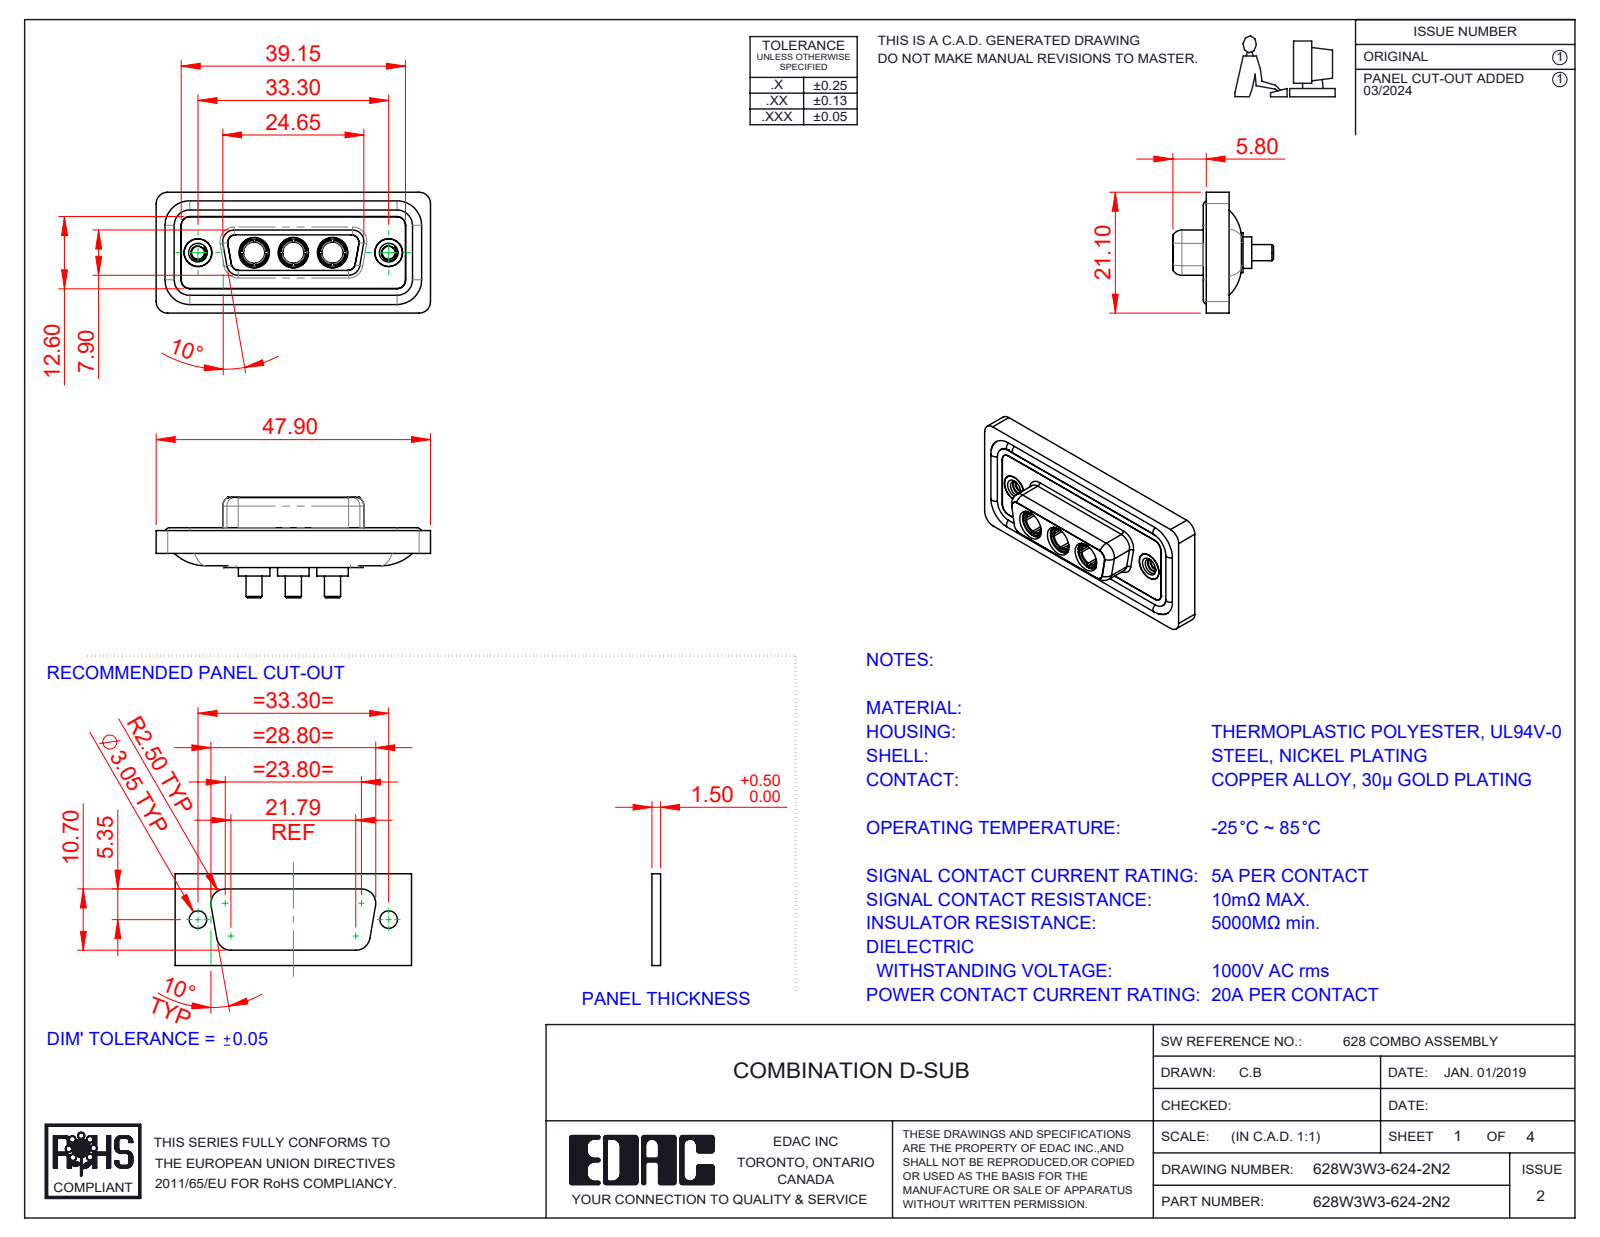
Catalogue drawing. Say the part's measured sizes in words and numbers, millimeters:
The part is named "628Combo Housing_3W3; 628Combo Threaded Rivet_2; 628Combo Waterproof Housing_15 Contacts; 628Combo Shell Rear_15 Contacts (+3 more)". Its 3-D file was written by "SolidWorks 2023 (CONFIG_CONTROL_DESIGN)". It is 13 solids with 608 faces: 192 planar, 257 cylindrical and 159 other. Overall it measures 47.9 by 21.1 by 17.55 millimeters. Its volume is 6 026 cubic millimeters and its surface area 9 739 square millimeters. Round holes: 5 of diameter 4.85, 3 of diameter 3.7, 3 of diameter 5.3, 2 of diameter 2.26, 2 of diameter 4, 2 of diameter 4.05, 2 of diameter 5. Round bosses or shafts: 4 of diameter 1.6, 3 of diameter 5.5, 3 of diameter 5.2, 3 of diameter 4.96, 3 of diameter 4.75, 3 of diameter 3.75, 3 of diameter 2.8, 2 of diameter 4.95. Partial cylindrical surfaces (rounded edges, fillets, slot ends): 22 of radius 1.5, 20 of radius 2, 12 of radius 1.35, 8 of radius 1.6, 4 of radius 0.25, 4 of radius 0.5, 4 of radius 0.6, 4 of radius 0.65. The main face-to-face distances are 0.4, 1.8, 1.6, 0.5, 7.45, 1.1, 2.9, 5.65, 7.05, 6.6. The hole center spacings are 6.85, 9.8, 16.65, 23.5, 13.7, 33.3.
